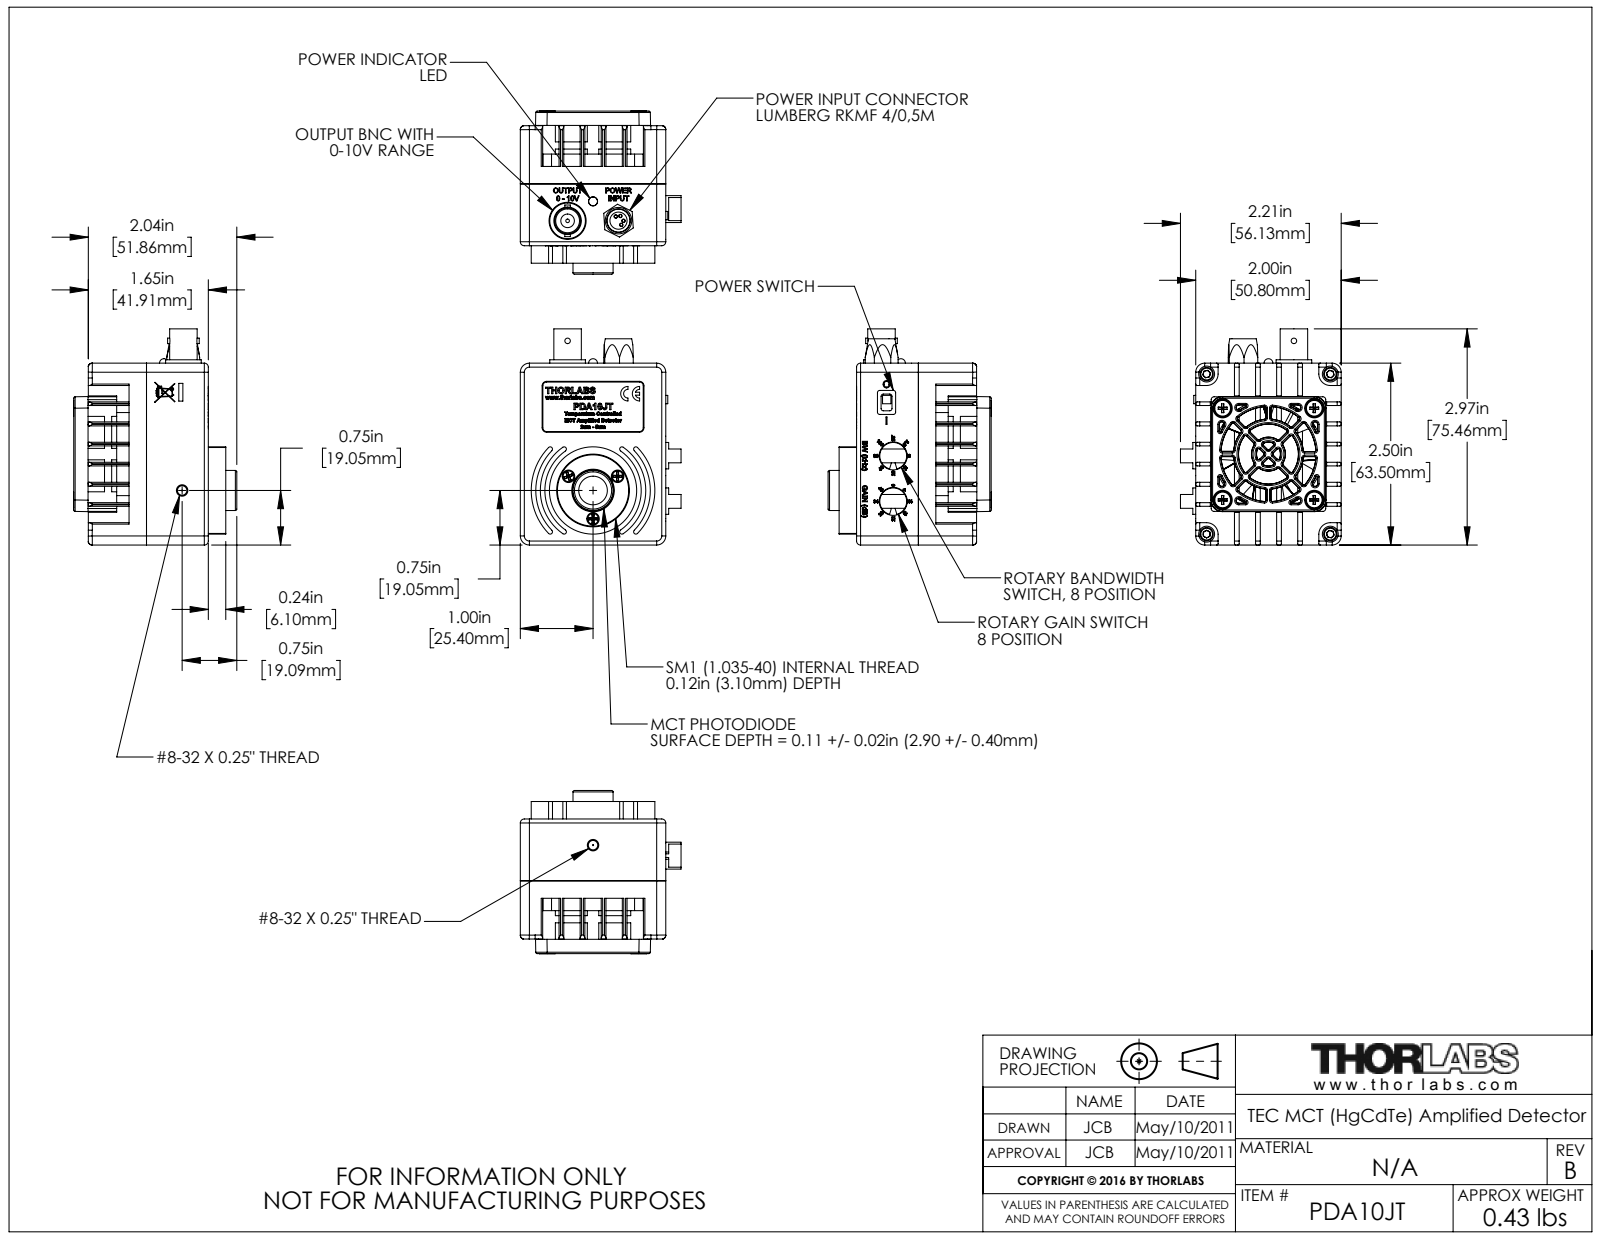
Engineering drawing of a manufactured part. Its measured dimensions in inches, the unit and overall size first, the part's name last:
Units: inches
Overall size (bounding box): 2.971 × 2.244 × 2.17
Round holes (diameter × count): ⌀0.037 ×14, ⌀0.086 ×11, ⌀0.096 ×9, ⌀0.07 ×8, ⌀0.022 ×6, ⌀0.031 ×6, ⌀0.059 ×6, ⌀0.063 ×6, ⌀0.05 ×5, ⌀0.015 ×4, ⌀0.032 ×4, ⌀0.039 ×4
Round bosses / shafts (diameter × count): ⌀0.14 ×8, ⌀0.018 ×6, ⌀0.217 ×4, ⌀0.183 ×4, ⌀0.125 ×4, ⌀0.118 ×4, ⌀0.038 ×4, ⌀0.018 ×4
Partial cylindrical surfaces — rounded edges, fillets, slot ends (radius × count): R0.005 ×154, R0.007 ×58, R0.02 ×48, R0.008 ×33, R0.01 ×31, R0.1 ×26, R0.02 ×24, R0.004 ×20
Main face-to-face distances: 0.24, 0.533, 0.05, 1.09, 0.065, 0.8, 0.483, 1.04, 0.85, 0.58
Hole centre spacings: 0.224, 1.256, 0.069, 0.317, 0.449, 0.463, 0.519, 1.214
Volume: 4.341 in³ · Surface area: 109.2 in²
Bodies: 115 solids, 9151 faces (5456 planar, 1646 cylindrical, 2049 other)
Part name (STEP PRODUCT): 21417-E0W
STEP written by: SolidWorks 2011 (CONFIG_CONTROL_DESIGN)
